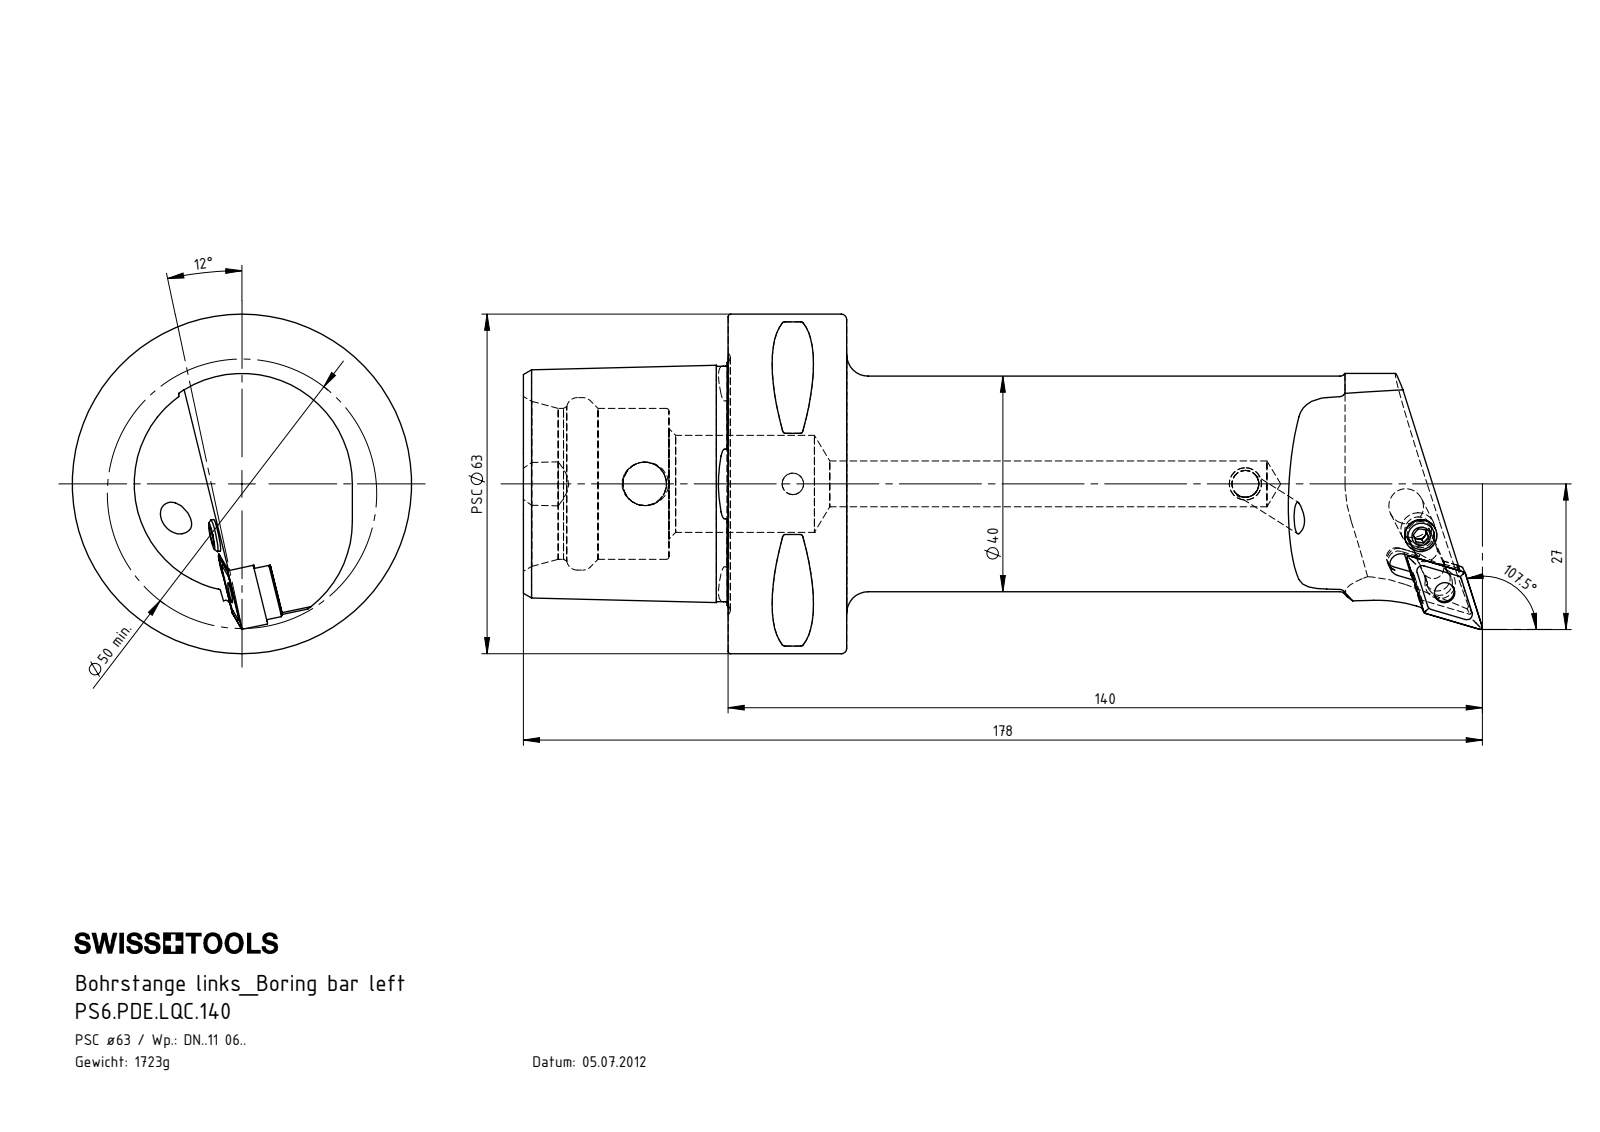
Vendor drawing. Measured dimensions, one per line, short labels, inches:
name: PS6-PDE.LQC.140; WDE-ER1.101.000; WDE-ER4.101.017_A; WDE-ER2.101.003_A (+4 more)
written by: SolidWorks 2012 (CONFIG_CONTROL_DESIGN)
unit: in
bodies: 8 solids, 363 faces (109 planar, 81 cylindrical, 173 other)
size: 7.008 × 2.48 × 2.48
volume: 13.42 in³; area: 59.8 in²
holes: 3× ⌀0.197, 1× ⌀0.15, 1× ⌀0.157, 1× ⌀0.189, 1× ⌀0.252, 1× ⌀0.319, 1× ⌀0.335, 1× ⌀0.709, 1× ⌀1.102, 1× ⌀1.26
bosses: 2× ⌀0.236, 1× ⌀2.48, 1× ⌀1.575, 1× ⌀0.232, 1× ⌀0.113
rounds: 8× R0.016, 8× R0.02, 4× R0.083, 1× R0.072, 1× R0.073, 1× R0.089, 1× R0.093, 1× R0.094
face distances: 0.866, 1.496, 2.362, 0.98, 1.063, 0.433, 1.299, 2.197, 0.343, 0.182
hole spacings: 0.464, 1.083, 3.307, 4.39
